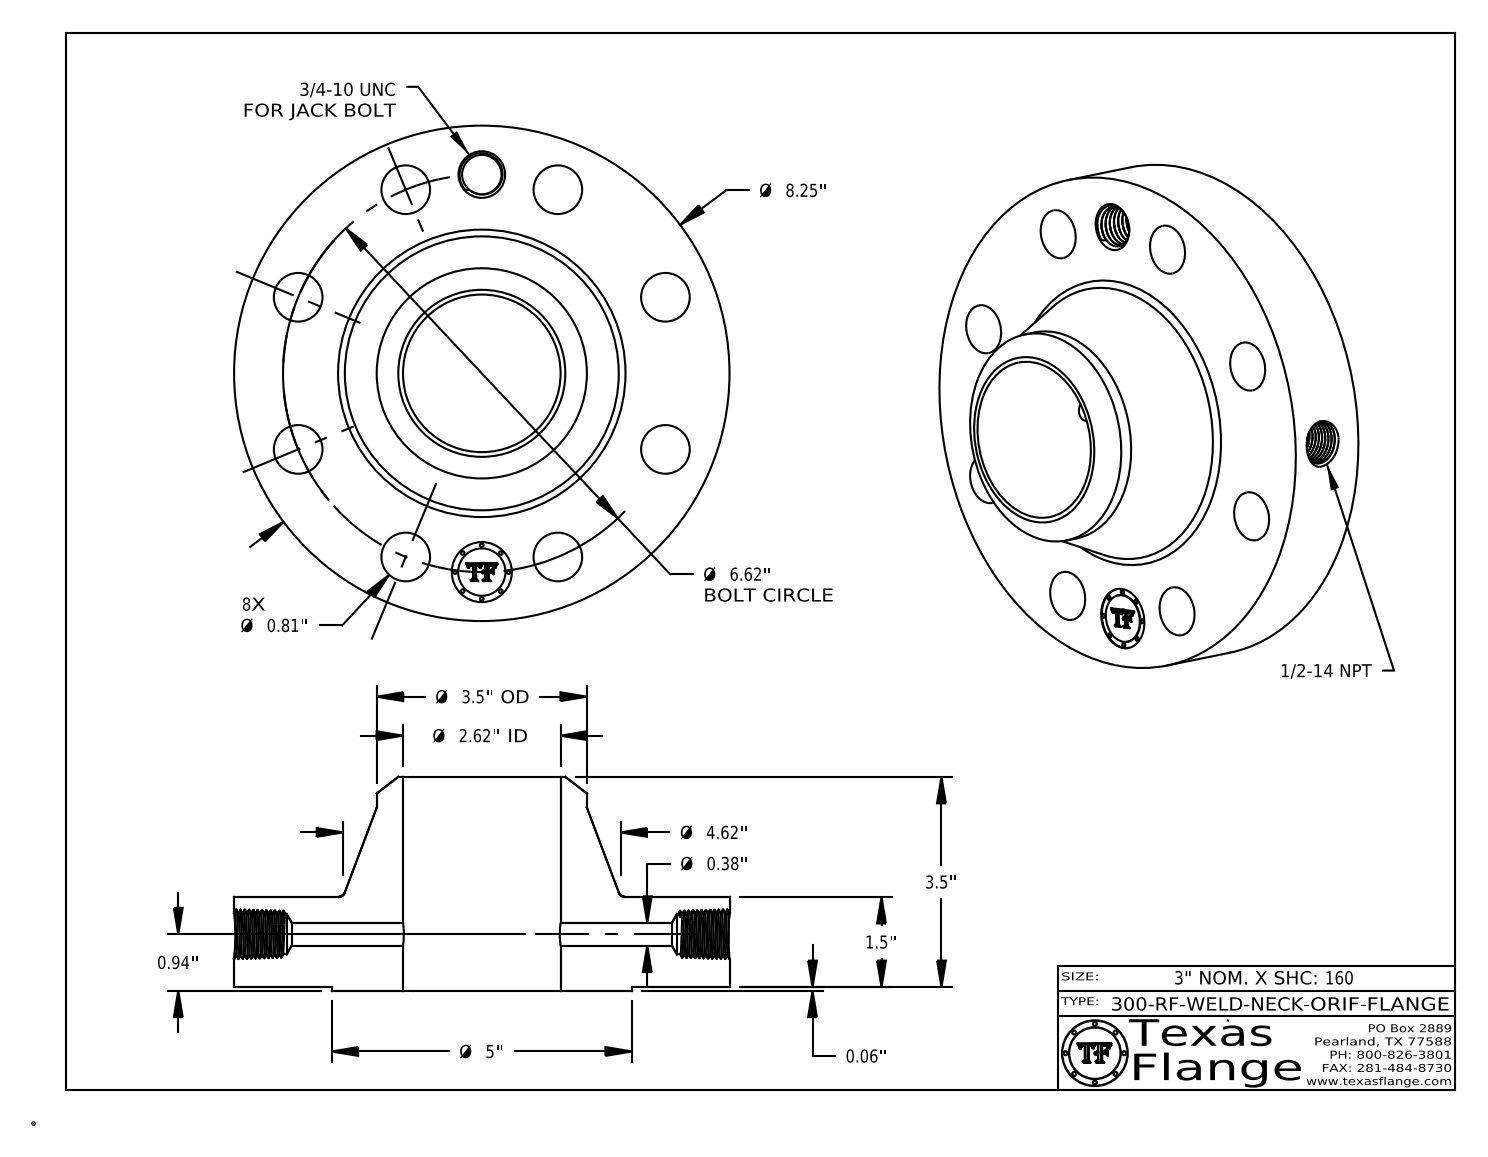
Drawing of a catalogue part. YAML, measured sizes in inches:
part_name: "300-RF-WELD-NECK"
step_written_by: "CATIA V5 STEP AP214 (AUTOMOTIVE_DESIGN)"
units: inches
bodies: {solids: 1, faces: 769, planar: 369, cylindrical: 92, other: 308}
overall_size: [8.25, 8.25, 3.56]
volume: 77.96
surface_area: 218.8
round_holes:
  - {diameter: 0.81, count: 8}
  - {diameter: 0.38, count: 1}
  - {diameter: 0.656, count: 1}
  - {diameter: 0.672, count: 1}
  - {diameter: 1, count: 1}
  - {diameter: 2.624, count: 1}
round_bosses_or_shafts:
  - {diameter: 0.061, count: 8}
  - {diameter: 8.25, count: 1}
  - {diameter: 5, count: 1}
  - {diameter: 3.5, count: 1}
  - {diameter: 0.788, count: 1}
face_to_face_distances: [1.5, 0.06, 1.56, 3.56, 3.5, 2, 0.015, 1.545, 1.485, 2.015]
hole_center_spacings: [3.31, 4.681, 6.116, 6.62, 1.291, 2.533, 2.533, 3.678]
